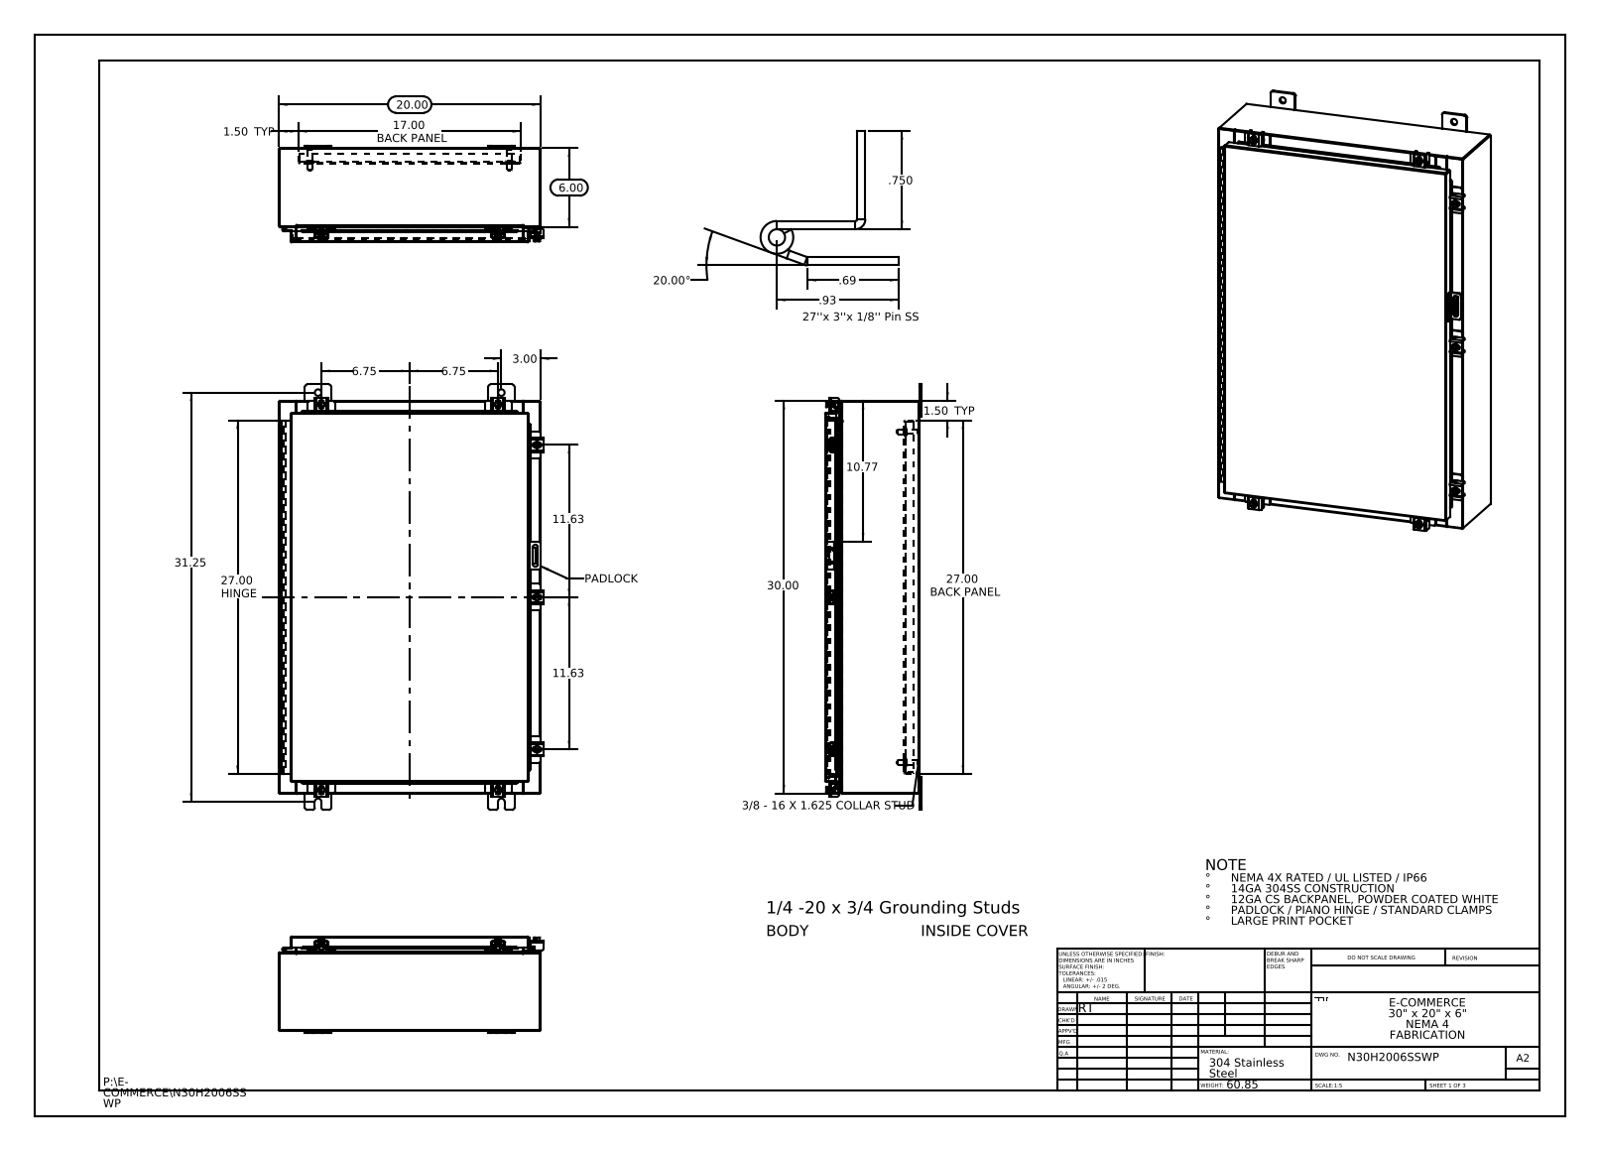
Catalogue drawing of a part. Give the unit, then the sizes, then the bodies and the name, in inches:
Units: inches
Overall size (bounding box): 32.5 × 20.211 × 7.389
Round holes (diameter × count): ⌀0.5 ×8, ⌀0.213 ×7, ⌀0.26 ×7, ⌀0.125 ×2, ⌀0.125 ×1
Round bosses / shafts (diameter × count): ⌀0.25 ×8, ⌀0.5 ×7, ⌀0.399 ×7, ⌀0.625 ×4, ⌀0.375 ×4, ⌀0.33 ×4
Partial cylindrical surfaces — rounded edges, fillets, slot ends (radius × count): R0.06 ×34, R0.013 ×27, R0.19 ×24, R0.088 ×21, R0.12 ×14, R0.141 ×14, R0.05 ×11, R0.08 ×10
Main face-to-face distances: 0.075, 7.126, 7.201, 7.051, 0.104, 1, 1.075, 6.051, 6.126, 1.179
Hole centre spacings: 27.365, 30.898, 0.431, 0.934, 1.858, 2.275, 2.276, 2.327
Volume: 214.2 in³ · Surface area: 5 347 in²
Bodies: 52 solids, 1990 faces (1056 planar, 830 cylindrical, 104 other)
Part name (STEP PRODUCT): N30H2006SSWP Top; N30H2006SSWP Hinge Cover Side; N30H2006SSWP Body; N30H2006SSWP (+8 more)
STEP written by: SolidWorks 2013 (CONFIG_CONTROL_DESIGN)
